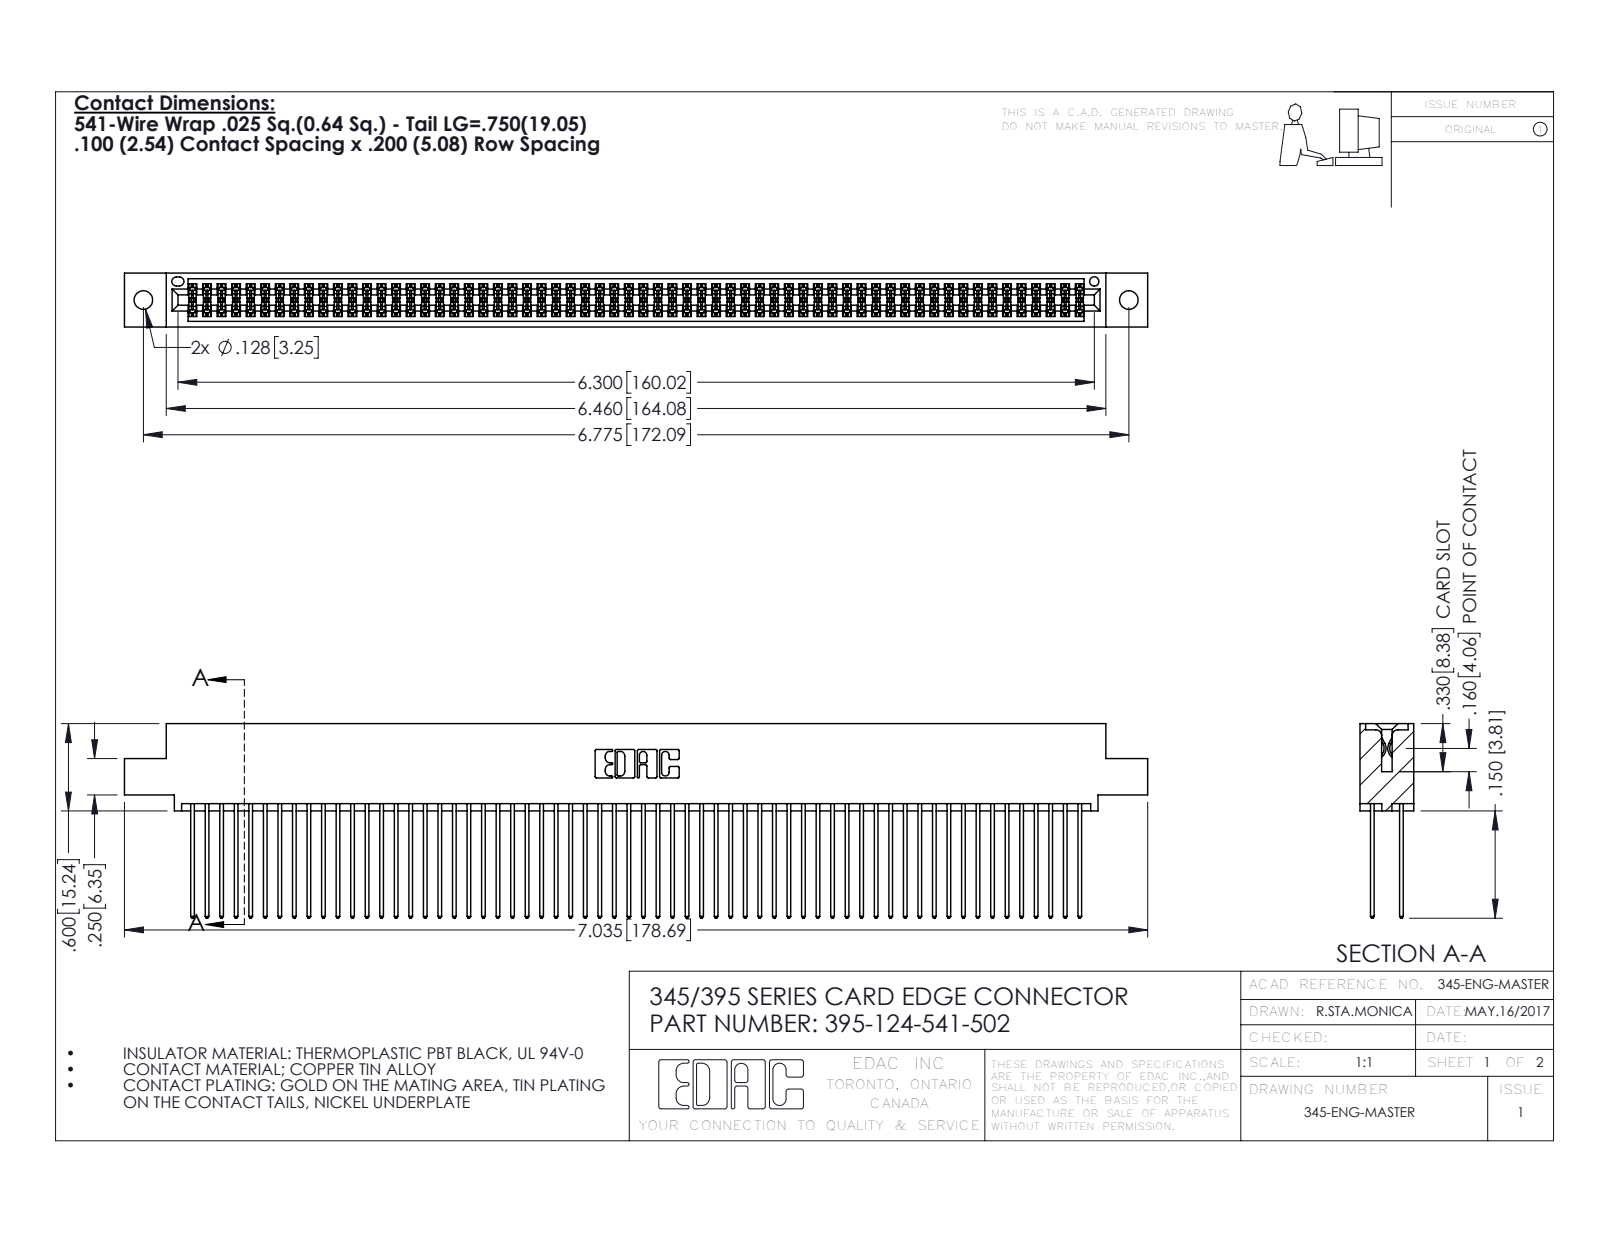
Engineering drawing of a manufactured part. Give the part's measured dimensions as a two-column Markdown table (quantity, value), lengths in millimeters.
| quantity | value |
| --- | --- |
| part name | 395-124-541-502; 345-292-001_345-293-141; 345 Part_0.110 Offset - 0.128 Dia |
| STEP written by | SolidWorks 2016 (CONFIG_CONTROL_DESIGN) |
| units | millimeters |
| bodies | 125 solids, 6330 faces (4176 planar, 2154 cylindrical, 0 other) |
| overall size | 178.7 × 34 × 9.4 |
| volume | 18 140 mm³ |
| surface area | 30 370 mm² |
| round holes (diameter × count) | 3.3 × 2, 1.6 × 1 |
| partial cylindrical surfaces (radius × count) | 0.2 × 186, 0.3 × 124, 0.3 × 22, 0.2 × 6, 0.8 × 6, 0.7 × 3, 0.4 × 2, 0.5 × 2 |
| main face-to-face distances | 1.8, 7.6, 5.1, 2.5, 6.9, 0.6, 5.7, 9.4, 4.4, 3.8 |
| hole center spacings | 6.9, 166.1, 172.1 |
